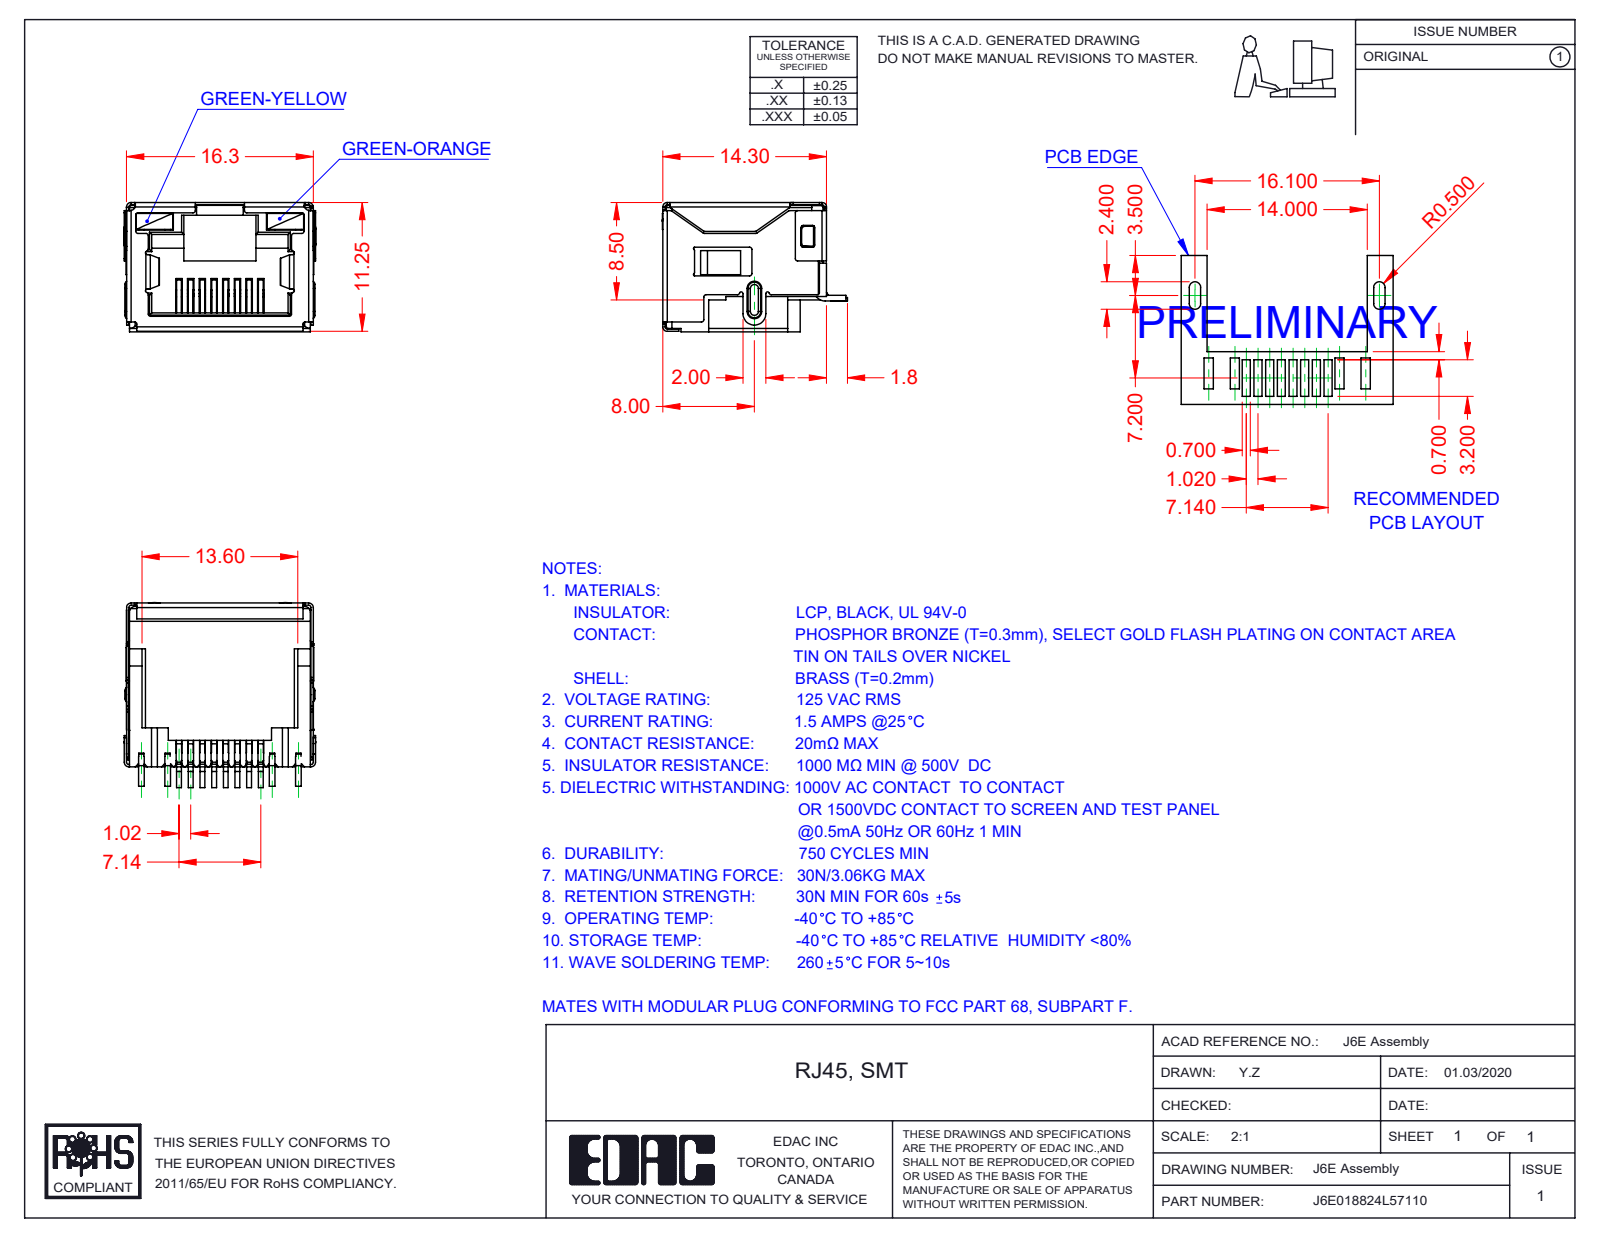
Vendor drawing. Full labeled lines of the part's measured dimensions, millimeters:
Part name (STEP PRODUCT): 6E Shield_LED; 6E Contacts; J6E018824L57110; 6E LED LH_5-Green-Yellow (+2 more)
STEP written by: SolidWorks 2016 (CONFIG_CONTROL_DESIGN)
Units: millimetres
Bodies: 12 solids, 1500 faces (1099 planar, 351 cylindrical, 50 other)
Overall size (bounding box): 16.75 × 16.15 × 11.3
Volume: 1 109 mm³ · Surface area: 4 045 mm²
Partial cylindrical surfaces — rounded edges, fillets, slot ends (radius × count): R0.2 ×82, R0.25 ×17, R0.4 ×13, R0.5 ×13, R0.1 ×10, R0.15 ×7, R0.3 ×4, R1 ×3
Main face-to-face distances: 11.05, 16.05, 16.1, 15.85, 11.1, 11.3, 2.4, 0.7, 9.85, 0.49
